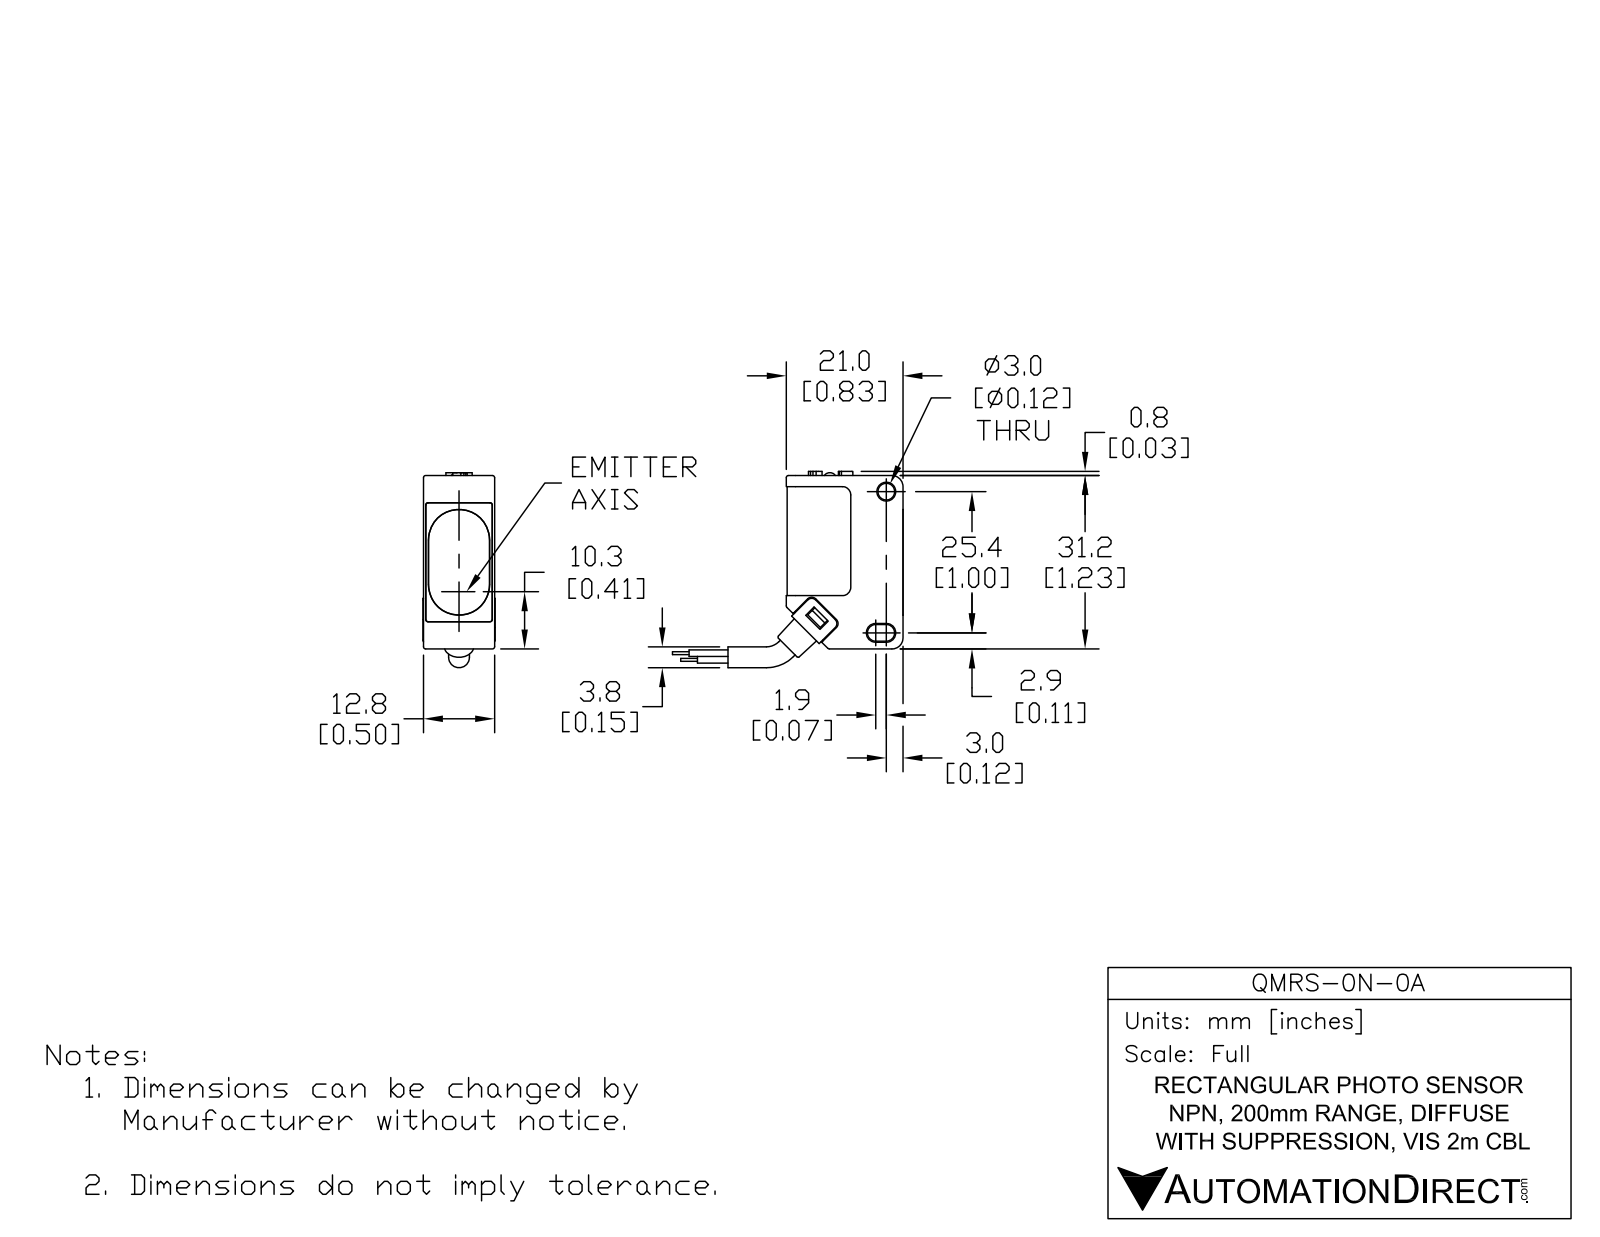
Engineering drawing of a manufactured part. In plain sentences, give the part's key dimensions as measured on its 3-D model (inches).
The part is named "QMRS-0N-0A". Its 3-D file was written by "SolidWorks 2017 (AUTOMOTIVE_DESIGN)". It is 9 solids with 248 faces: 132 planar, 92 cylindrical and 24 other. Overall it measures 3.193 by 1.032 by 0.512 inches. Its volume is 0.465 cubic inches and its surface area 8.347 square inches. Round holes: 1 of diameter 0.118, 1 of diameter 0.148, 1 of diameter 0.173, 1 of diameter 0.224, 1 of diameter 0.283. Round bosses or shafts: 1 of diameter 0.122, 1 of diameter 0.11. Partial cylindrical surfaces (rounded edges, fillets, slot ends): 13 of radius 0.016, 8 of radius 0.039, 7 of radius 0.059, 4 of radius 0.02, 4 of radius 0.024, 4 of radius 0.177, 2 of radius 0.035, 2 of radius 0.065. The main face-to-face distances are 0.498, 0.039, 0.02, 0.016, 0.504, 0.138, 0.488, 0.482, 0.098, 0.492.
